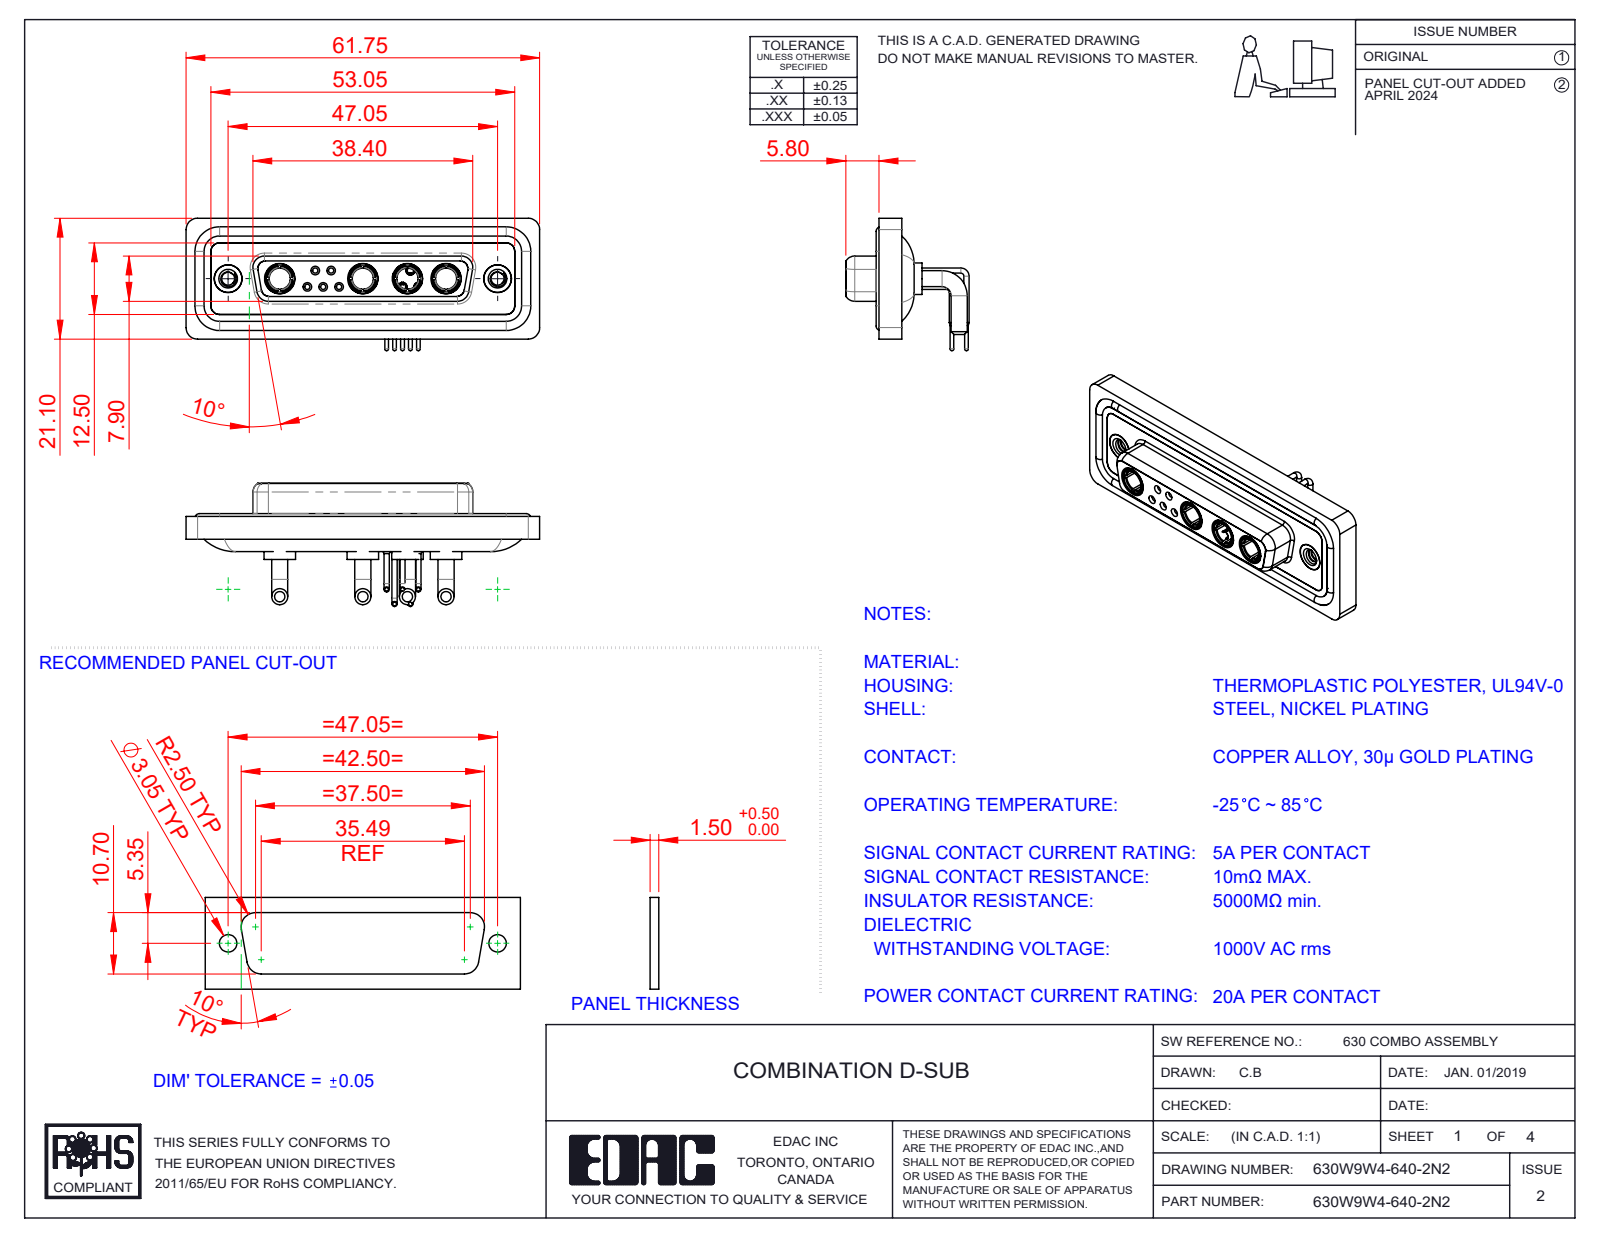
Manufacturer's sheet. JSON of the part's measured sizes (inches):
{"part_name": "630Combo Threaded Rivet_2; 630Combo Contact Row 1_50 Contacts; 630Combo Housing_9W4; 630W9W4-640-2N2 (+5 more)", "step_written_by": "SolidWorks 2023 (CONFIG_CONTROL_DESIGN)", "units": "inches", "bodies": {"solids": 20, "faces": 963, "planar": 296, "cylindrical": 403, "other": 264}, "overall_size": [2.431, 0.91, 0.848], "volume_in3": 0.516, "surface_area_in2": 21.77, "round_holes": [[0.191, 6], [0.035, 5], [0.043, 5], [0.059, 5], [0.079, 5], [0.146, 4], [0.209, 4], [0.063, 3], [0.067, 2], [0.089, 2], [0.157, 2], [0.159, 2]], "round_bosses_or_shafts": [[0.035, 10], [0.063, 9], [0.11, 8], [0.079, 5], [0.059, 5], [0.026, 5], [0.217, 4], [0.205, 4]], "partial_cylinders_radius": [[0.059, 18], [0.079, 18], [0.053, 8], [0.063, 8], [0.01, 4], [0.02, 4], [0.024, 4], [0.026, 4]], "face_to_face_distances": [0.016, 0.071, 0.161, 0.043, 0.059, 0.063, 0.098, 0.122, 0.146, 0.055], "hole_center_spacings": [0.124, 0.109, 0.198, 0.545, 0.436, 0.504, 0.61, 0.218]}
